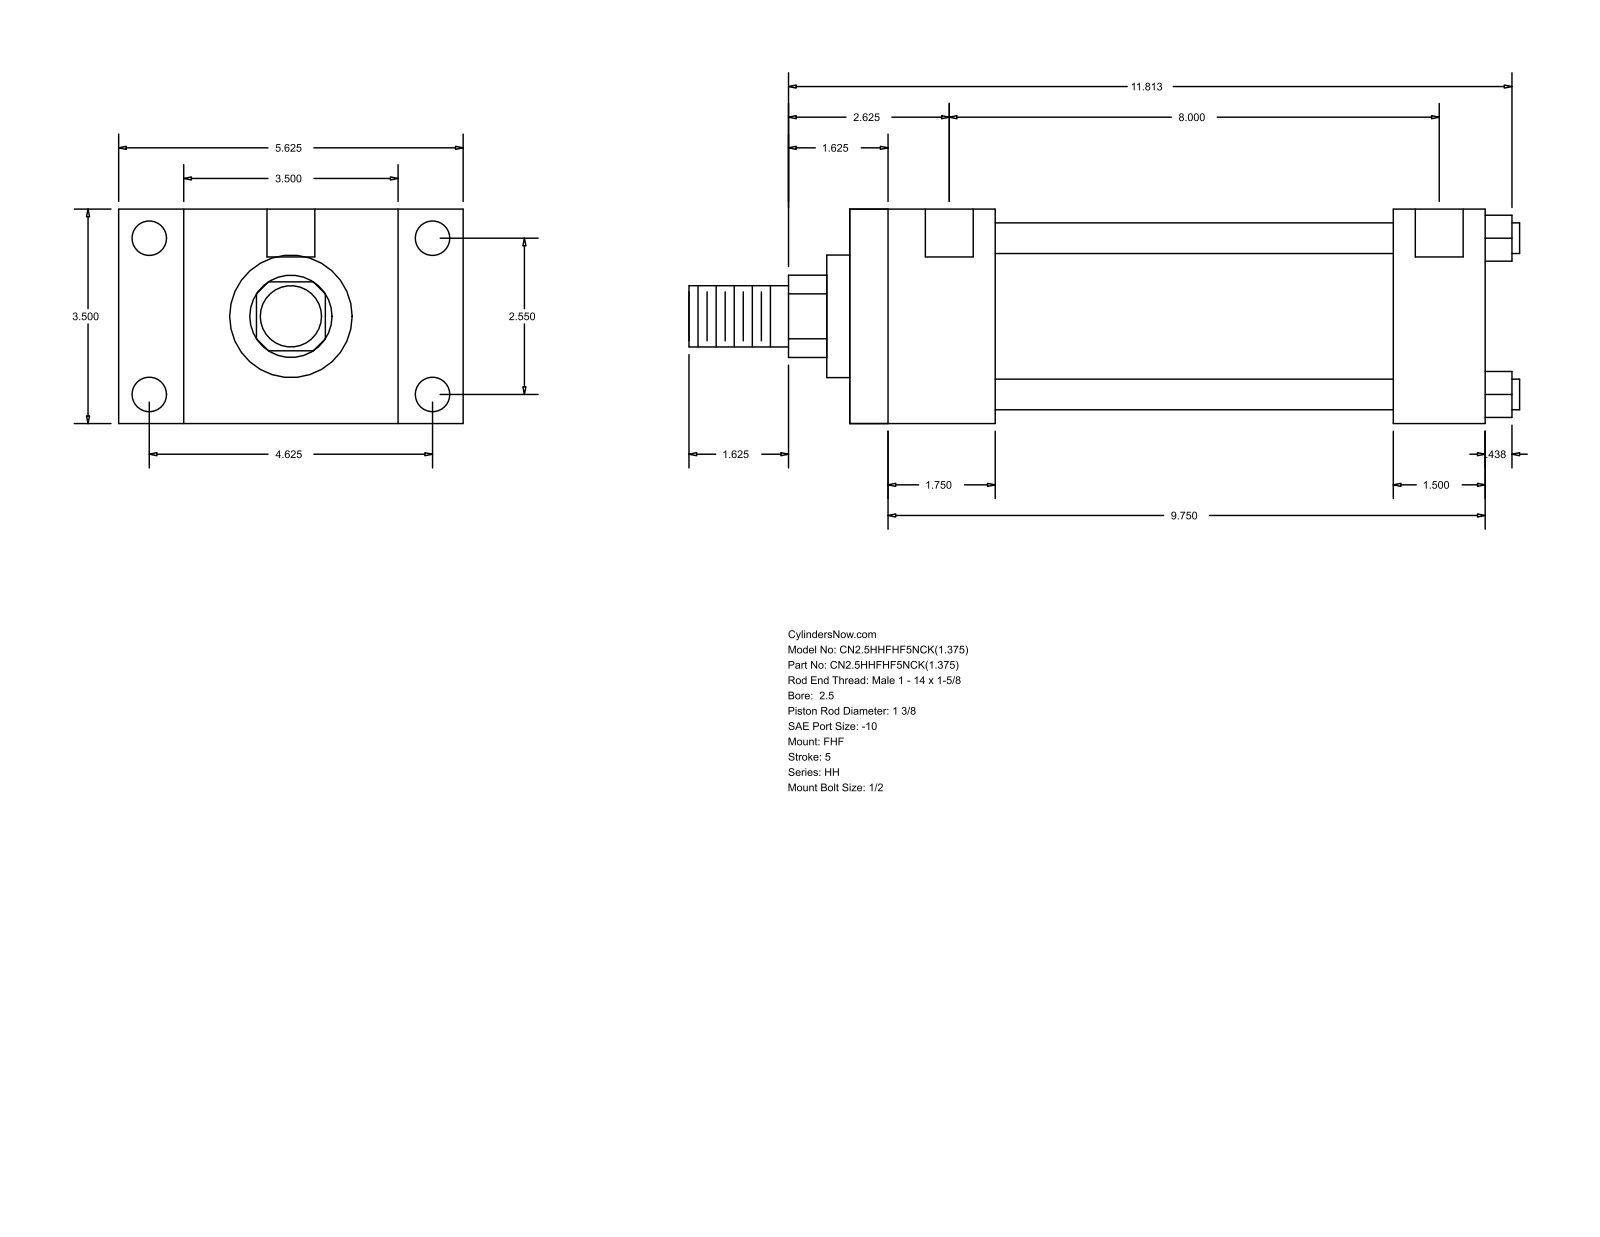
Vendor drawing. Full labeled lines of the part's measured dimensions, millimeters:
Part name (STEP PRODUCT): HH_FHF__0250_1.375
STEP written by: GSSL Pune (CONFIG_CONTROL_DESIGN)
Units: millimetres
Bodies: 0 solids, 88 faces (60 planar, 28 cylindrical, 0 other)
Overall size (bounding box): 344.49 × 142.88 × 88.9
Round holes (diameter × count): ⌀5.56 ×4, ⌀14.3 ×4, ⌀19.84 ×2
Round bosses / shafts (diameter × count): ⌀12.7 ×4, ⌀73.03 ×1, ⌀50.8 ×1, ⌀34.92 ×1, ⌀25.4 ×1
Partial cylindrical surfaces — rounded edges, fillets, slot ends (radius × count): R17.06 ×1
Main face-to-face distances: 88.9, 60.32, 26.99, 115.89, 263.53, 203.21, 142.88, 225.42, 165.1, 38.11
Hole centre spacings: 1.58, 64.76, 117.48, 134.15, 204.79, 206.37, 203.21
